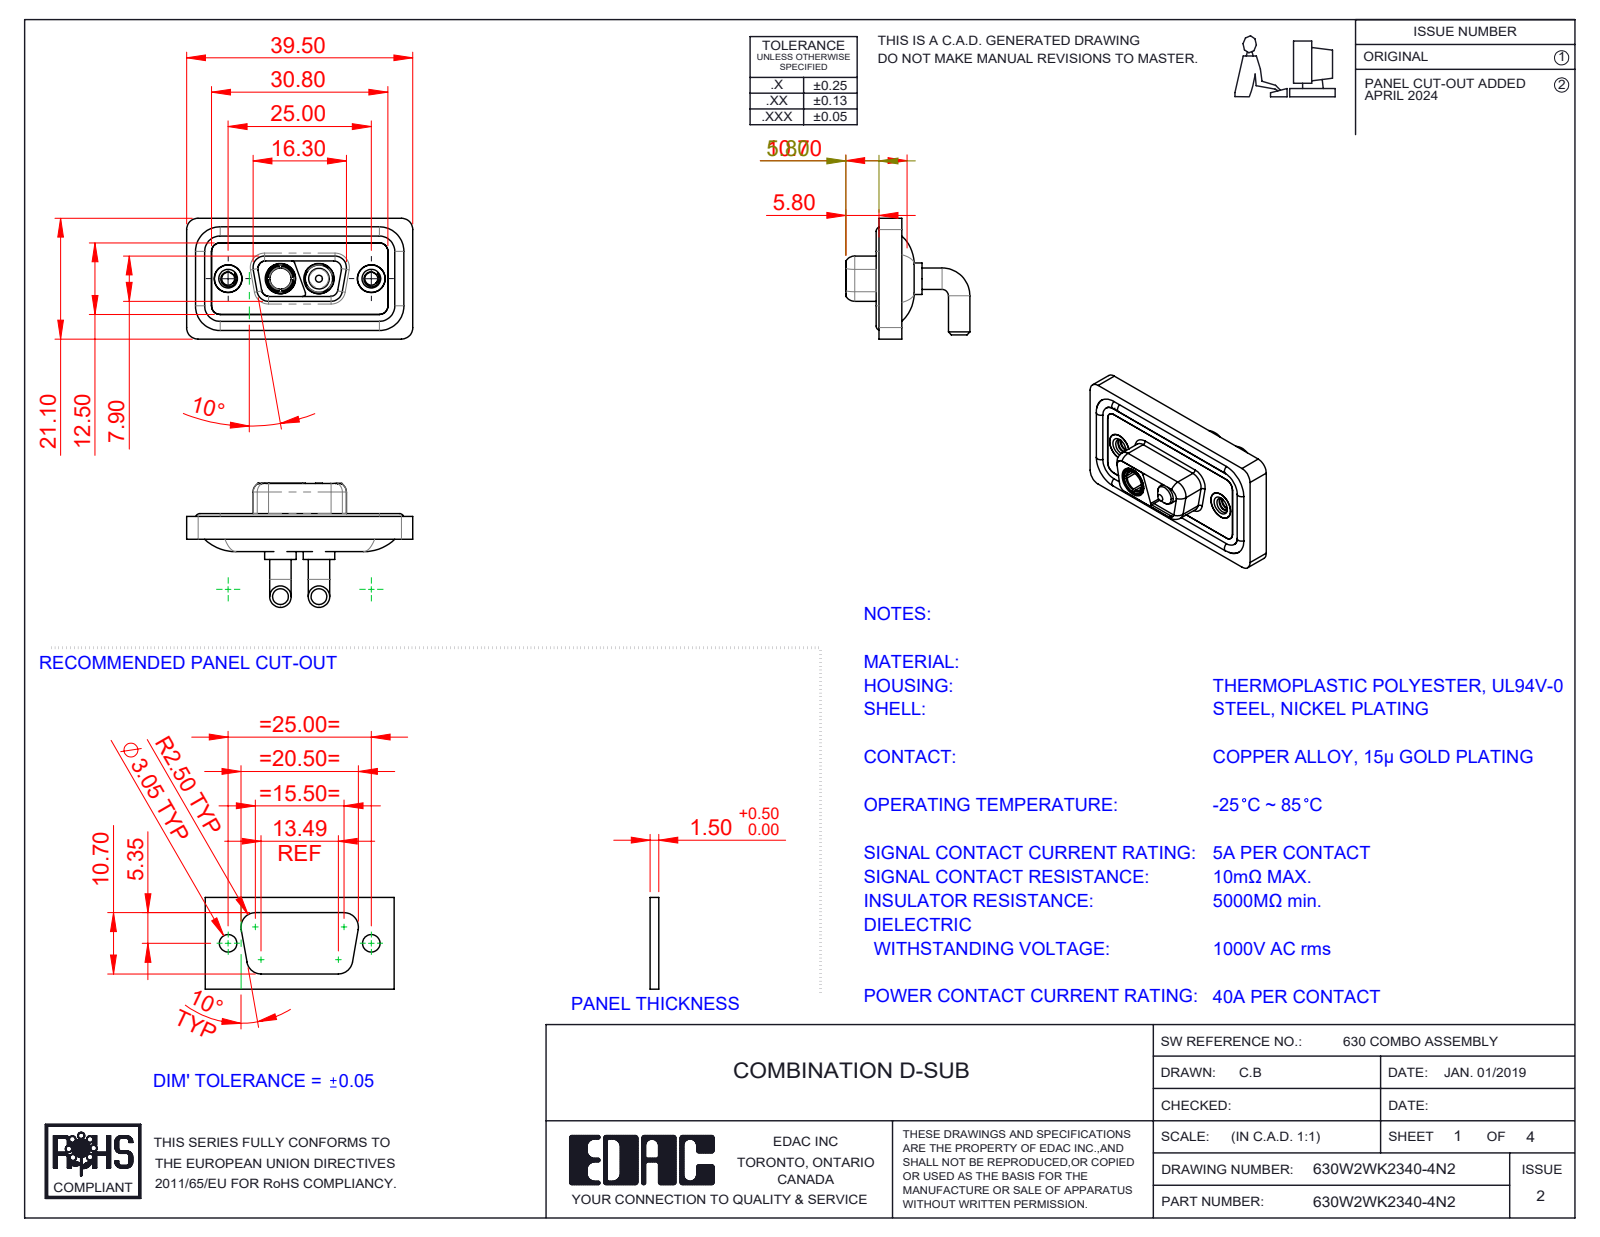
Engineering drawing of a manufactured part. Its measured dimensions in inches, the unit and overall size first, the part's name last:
Units: inches
Overall size (bounding box): 1.555 × 0.854 × 0.831
Round holes (diameter × count): ⌀0.191 ×4, ⌀0.089 ×2, ⌀0.157 ×2, ⌀0.159 ×2, ⌀0.197 ×2, ⌀0.209 ×2, ⌀0.146 ×1
Round bosses / shafts (diameter × count): ⌀0.148 ×4, ⌀0.063 ×4, ⌀0.217 ×2, ⌀0.205 ×2, ⌀0.195 ×2, ⌀0.189 ×2, ⌀0.187 ×2, ⌀0.195 ×1
Partial cylindrical surfaces — rounded edges, fillets, slot ends (radius × count): R0.059 ×18, R0.079 ×18, R0.053 ×8, R0.063 ×8, R0.02 ×6, R0.01 ×4, R0.024 ×4, R0.026 ×4
Main face-to-face distances: 0.016, 0.043, 0.114, 0.071, 0.098, 0.063, 0.122, 0.083, 0.146, 0.059
Hole centre spacings: 0.36, 0.624, 0.265, 0.984
Volume: 0.296 in³ · Surface area: 11.75 in²
Bodies: 11 solids, 508 faces (144 planar, 235 cylindrical, 129 other)
Part name (STEP PRODUCT): 630Combo Threaded Rivet_2; 630W2WK2340-4N2; 630Combo Housing_2WK2; Power Pin_40A RA (+4 more)
STEP written by: SolidWorks 2023 (CONFIG_CONTROL_DESIGN)
